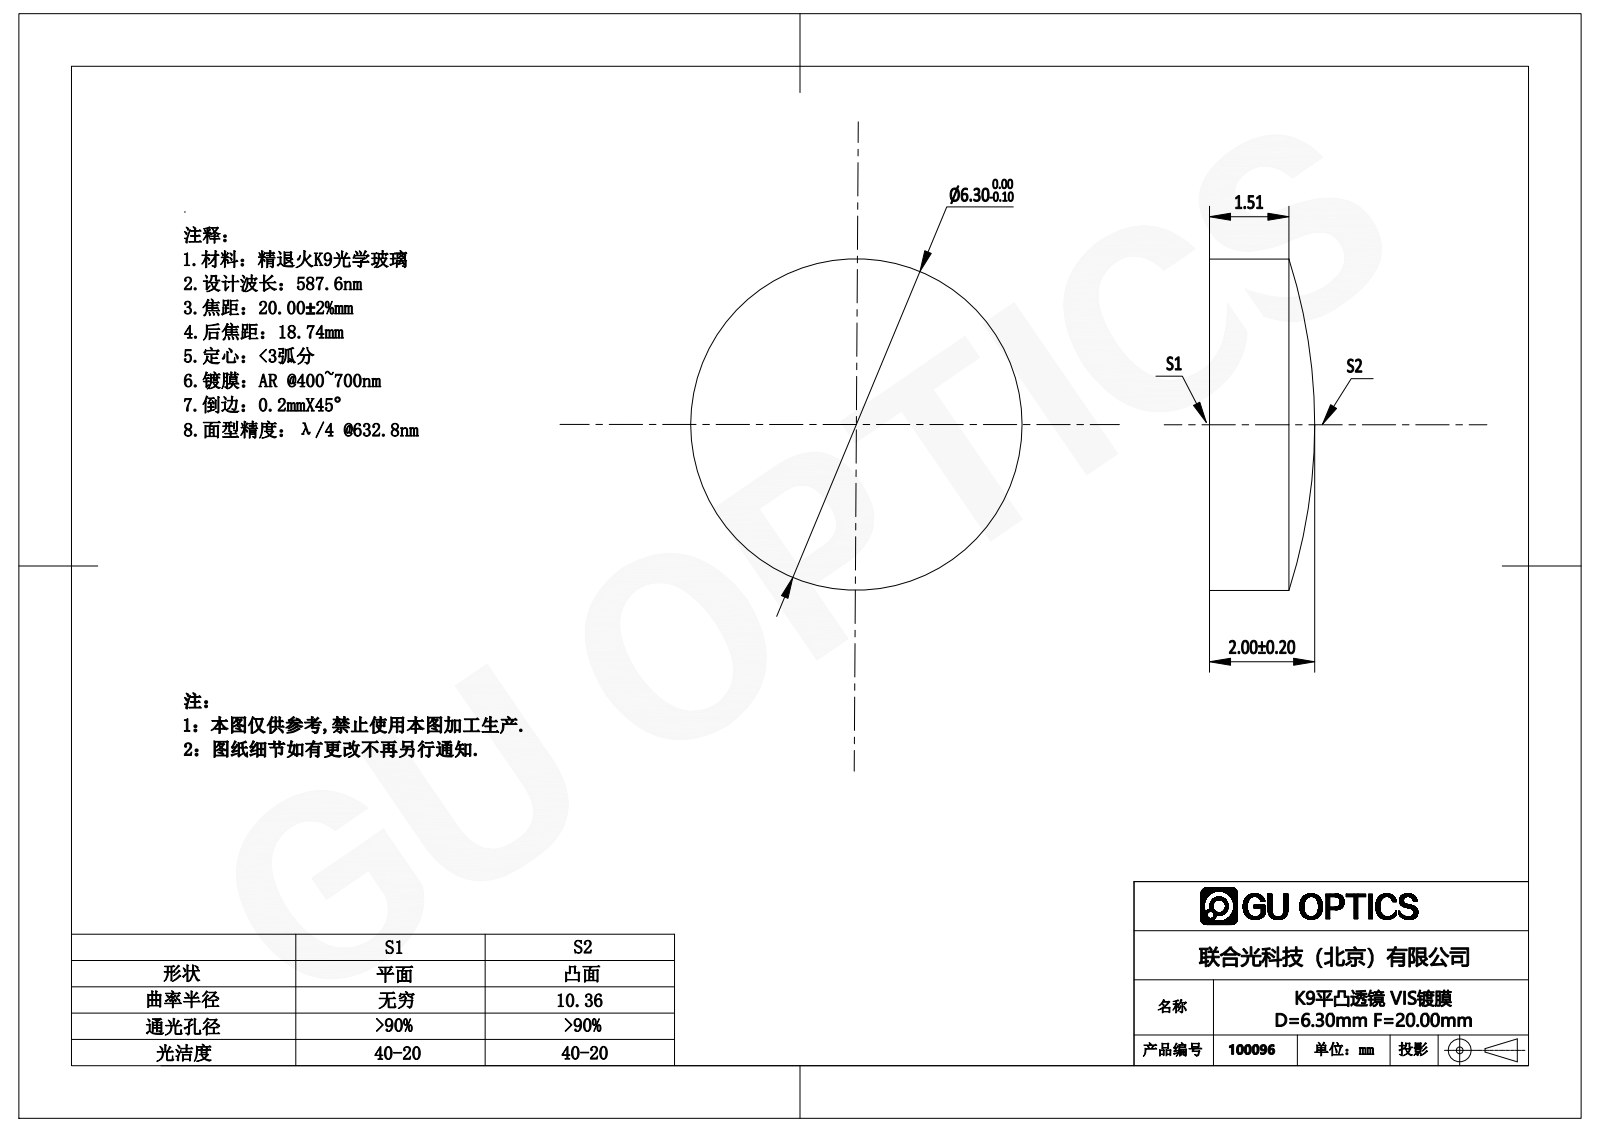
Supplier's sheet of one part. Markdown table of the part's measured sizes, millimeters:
| quantity | value |
| --- | --- |
| part name | 100096 |
| STEP written by | SolidWorks 2016 (AUTOMOTIVE_DESIGN) |
| units | millimeters |
| bodies | 1 solid, 5 faces (1 planar, 2 cylindrical, 2 other) |
| overall size | 6.3 × 6.3 × 2 |
| volume | 55 mm³ |
| surface area | 93 mm² |
| round bosses / shafts (diameter × count) | 6.3 × 1 |
